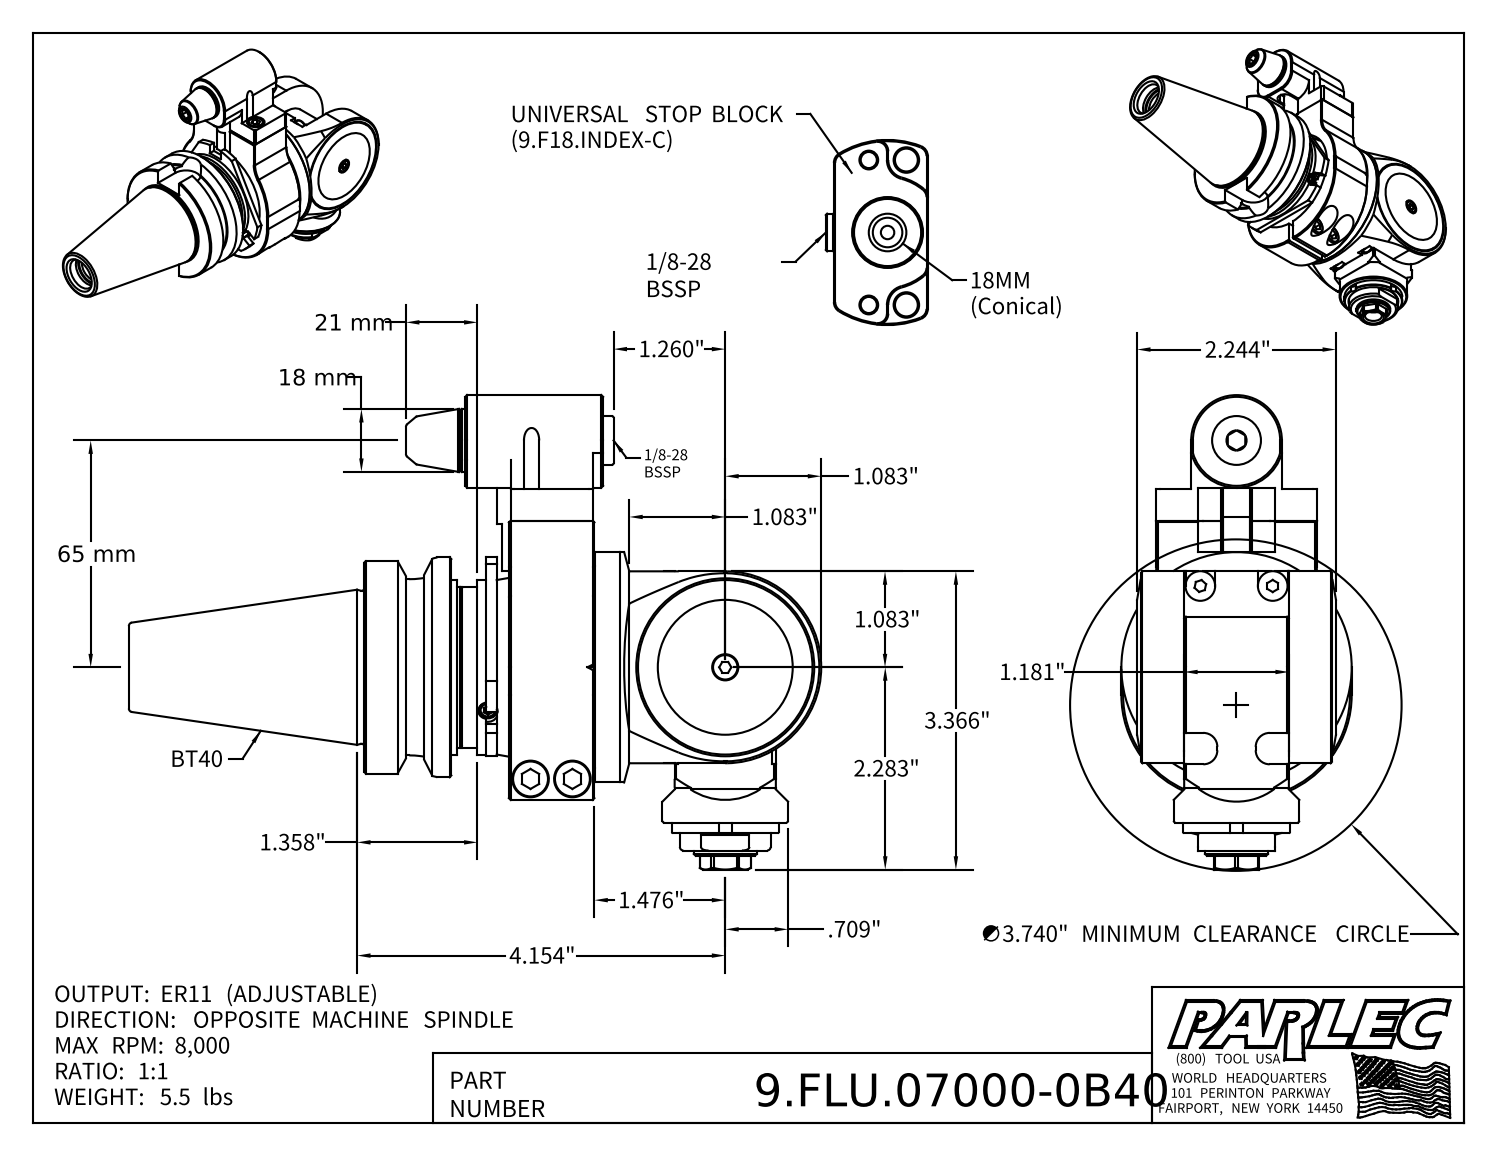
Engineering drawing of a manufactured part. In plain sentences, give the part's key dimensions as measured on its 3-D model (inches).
The part is named "9.FLU.07000-0B40; 9_GA0_346_2 (Type 0, BT40, 65mm); 9_FLU_07000". Its 3-D file was written by "Autodesk Inventor 2022 (AUTOMOTIVE_DESIGN)". It is 6 solids with 604 faces: 344 planar, 141 cylindrical and 119 other. Overall it measures 7.811 by 5.354 by 2.598 inches. Its volume is 28.49 cubic inches and its surface area 153.7 square inches. Round holes: 4 of diameter 0.295, 2 of diameter 0.217, 2 of diameter 0.37, 2 of diameter 0.413, 1 of diameter 0.165, 1 of diameter 0.205, 1 of diameter 0.236, 1 of diameter 0.315, 1 of diameter 0.335, 1 of diameter 0.354, 1 of diameter 0.425, 1 of diameter 0.457. Round bosses or shafts: 6 of diameter 0.335, 3 of diameter 0.394, 3 of diameter 0.276, 2 of diameter 0.709, 2 of diameter 0.236, 1 of diameter 2.598, 1 of diameter 2.591, 1 of diameter 2.48. Partial cylindrical surfaces (rounded edges, fillets, slot ends): 6 of radius 0.157, 4 of radius 0.039, 4 of radius 0.083, 4 of radius 0.197, 3 of radius 0.512, 2 of radius 0.315, 2 of radius 1.181, 1 of radius 0.287. The main face-to-face distances are 1.496, 0.315, 1.811, 1.319, 0.217, 1.181, 0.354, 0.531, 1.713, 0.965. The hole center spacings are 0.276, 0.014, 0.472, 0.551, 1.004, 1.457, 1.846, 1.859.
